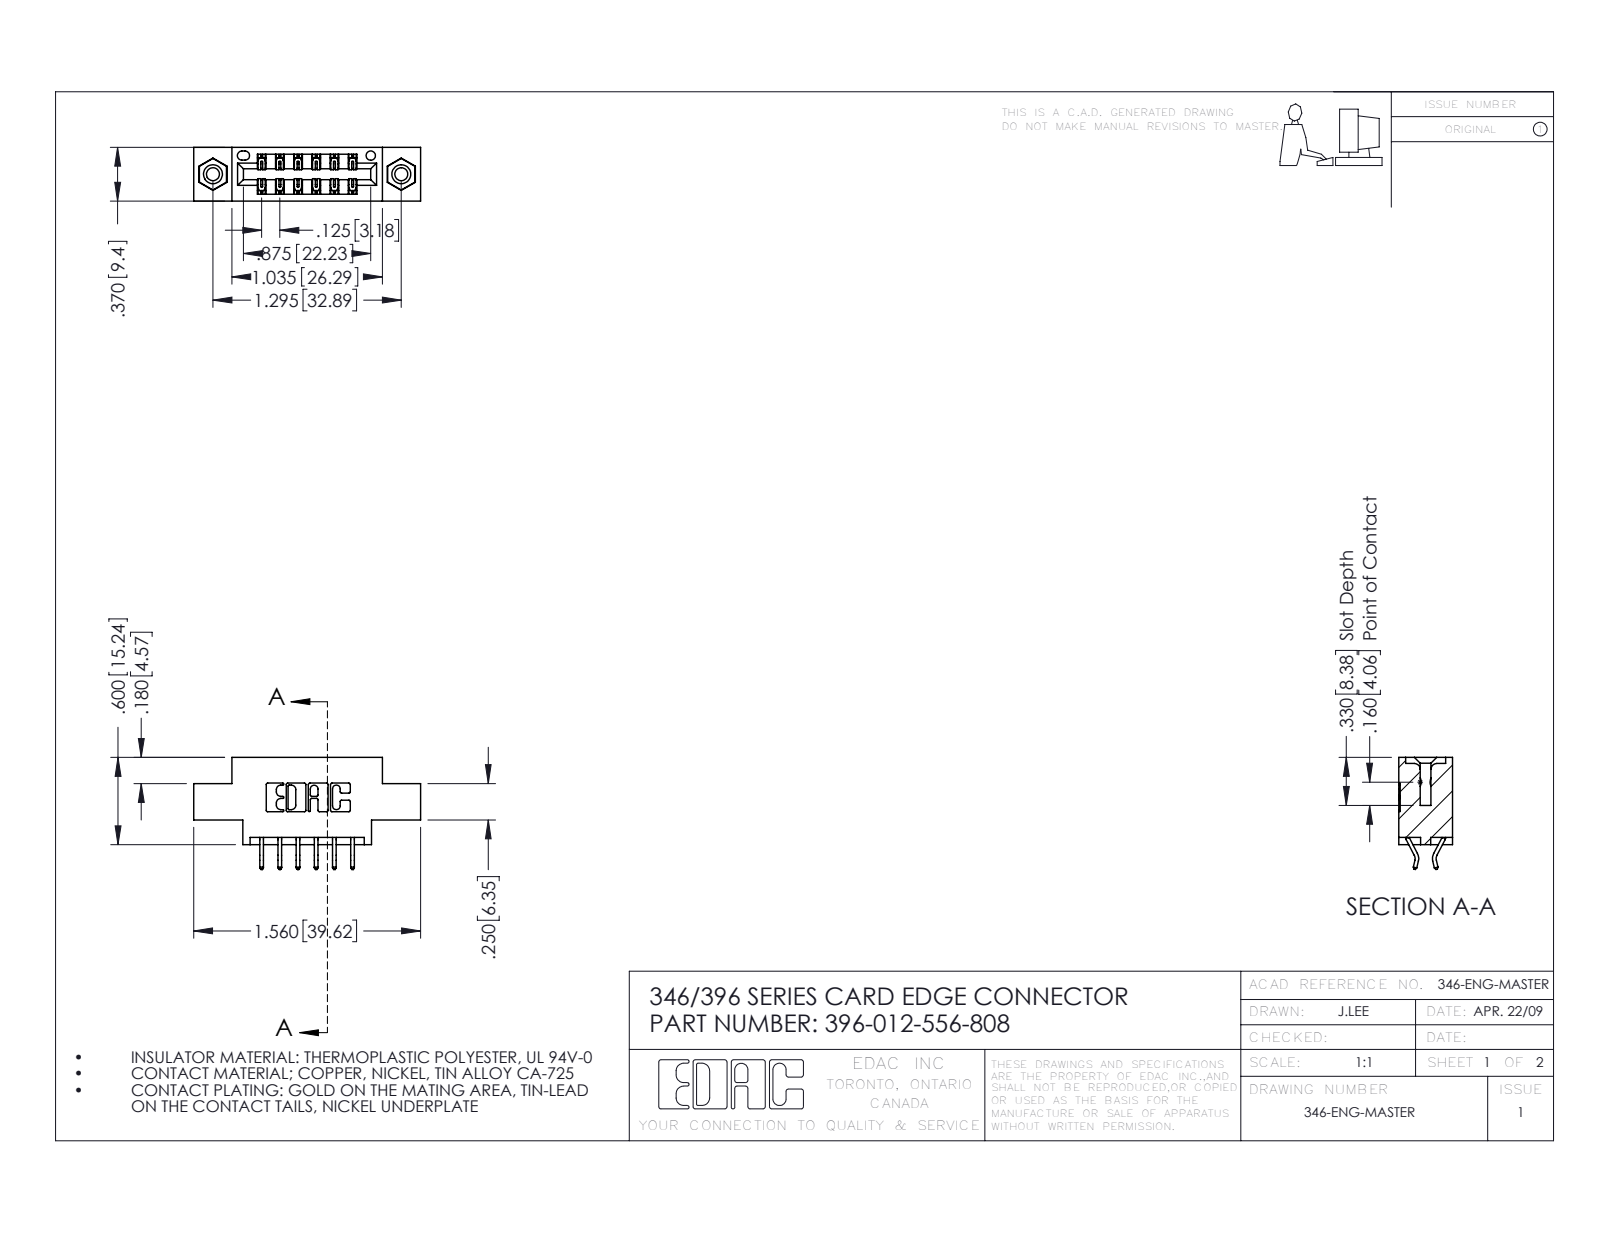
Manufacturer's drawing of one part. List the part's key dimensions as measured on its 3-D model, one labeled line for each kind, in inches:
Part name (STEP PRODUCT): 396-012-556-808; 345-292-001_556 Tail; 345-250-001_345-250-003-102; 346 Part_0.170 Offset - 0.156 Dia-TI
STEP written by: SolidWorks 2016 (CONFIG_CONTROL_DESIGN)
Units: inches
Bodies: 15 solids, 882 faces (580 planar, 286 cylindrical, 16 other)
Overall size (bounding box): 1.56 × 0.77 × 0.37
Volume: 0.209 in³ · Surface area: 6.707 in²
Round holes (diameter × count): ⌀0.089 ×2, ⌀0.125 ×2, ⌀0.156 ×2, ⌀0.064 ×1
Round bosses / shafts (diameter × count): ⌀0.155 ×2
Partial cylindrical surfaces — rounded edges, fillets, slot ends (radius × count): R0.01 ×22, R0.006 ×18, R0.007 ×6, R0.031 ×6, R0.026 ×3, R0.01 ×2, R0.014 ×2, R0.022 ×2
Main face-to-face distances: 0.25, 0.37, 0.048, 0.322, 0.222, 0.148, 0.1, 0.174, 0.025, 0.072
Hole centre spacings: 0.246, 1.092, 1.295
